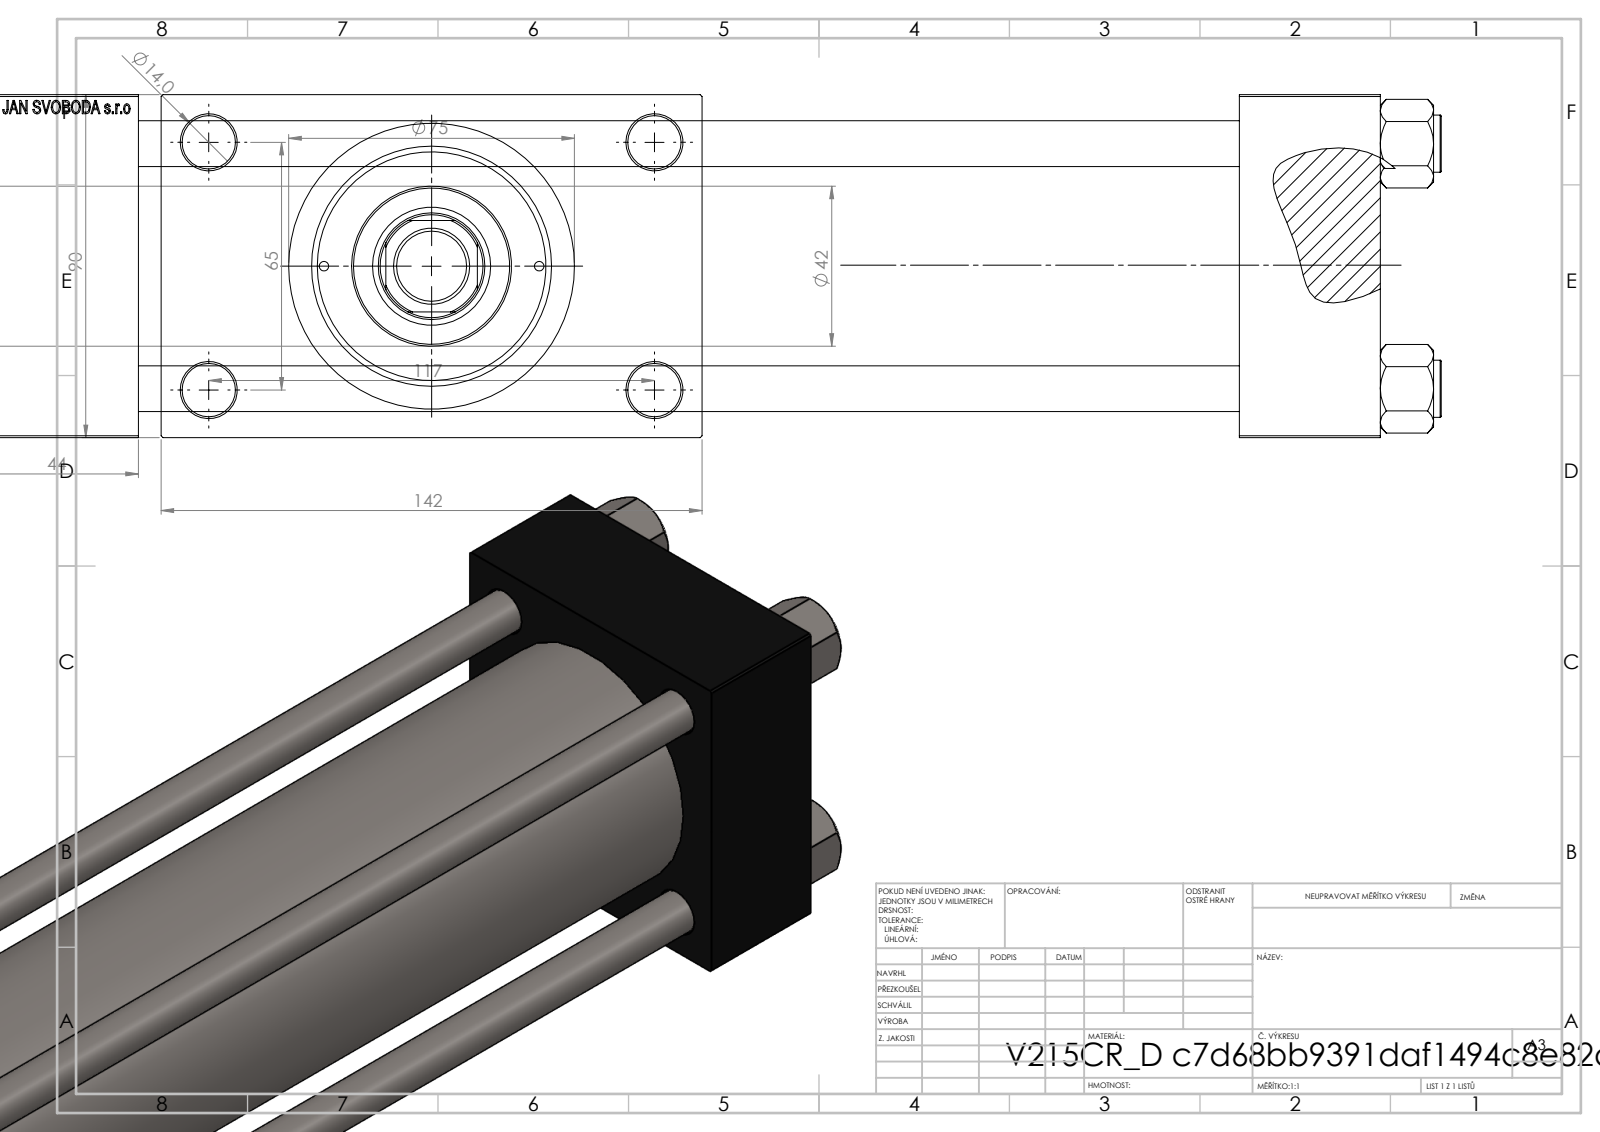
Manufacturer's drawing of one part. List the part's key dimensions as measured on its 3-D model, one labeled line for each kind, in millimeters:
Part name (STEP PRODUCT): ROD_END_AH; V215CR_VCP_D; V215CR_D_Body; V215CR_D_TYCINKA (+2 more)
STEP written by: SolidWorks 2019 (CONFIG_CONTROL_DESIGN)
Units: millimetres
Bodies: 12 solids, 1125 faces (503 planar, 96 cylindrical, 526 other)
Overall size (bounding box): 461 × 142 × 90
Volume: 1 493 000 mm³ · Surface area: 352 957 mm²
Round holes (diameter × count): ⌀12 ×4, ⌀14 ×4, ⌀2.5 ×2, ⌀7 ×2, ⌀20.96 ×2, ⌀30 ×2, ⌀18.5 ×1, ⌀28 ×1, ⌀31 ×1, ⌀50 ×1, ⌀60 ×1, ⌀63 ×1
Round bosses / shafts (diameter × count): ⌀15 ×4, ⌀75 ×1, ⌀69 ×1, ⌀42 ×1, ⌀20 ×1, ⌀18 ×1
Partial cylindrical surfaces — rounded edges, fillets, slot ends (radius × count): R13.5 ×1
Main face-to-face distances: 90, 289, 37, 326, 333, 370, 44, 26, 116, 16
Hole centre spacings: 26.35, 32.39, 44.4, 45.47, 64.3, 66.92, 68.42, 69.81
